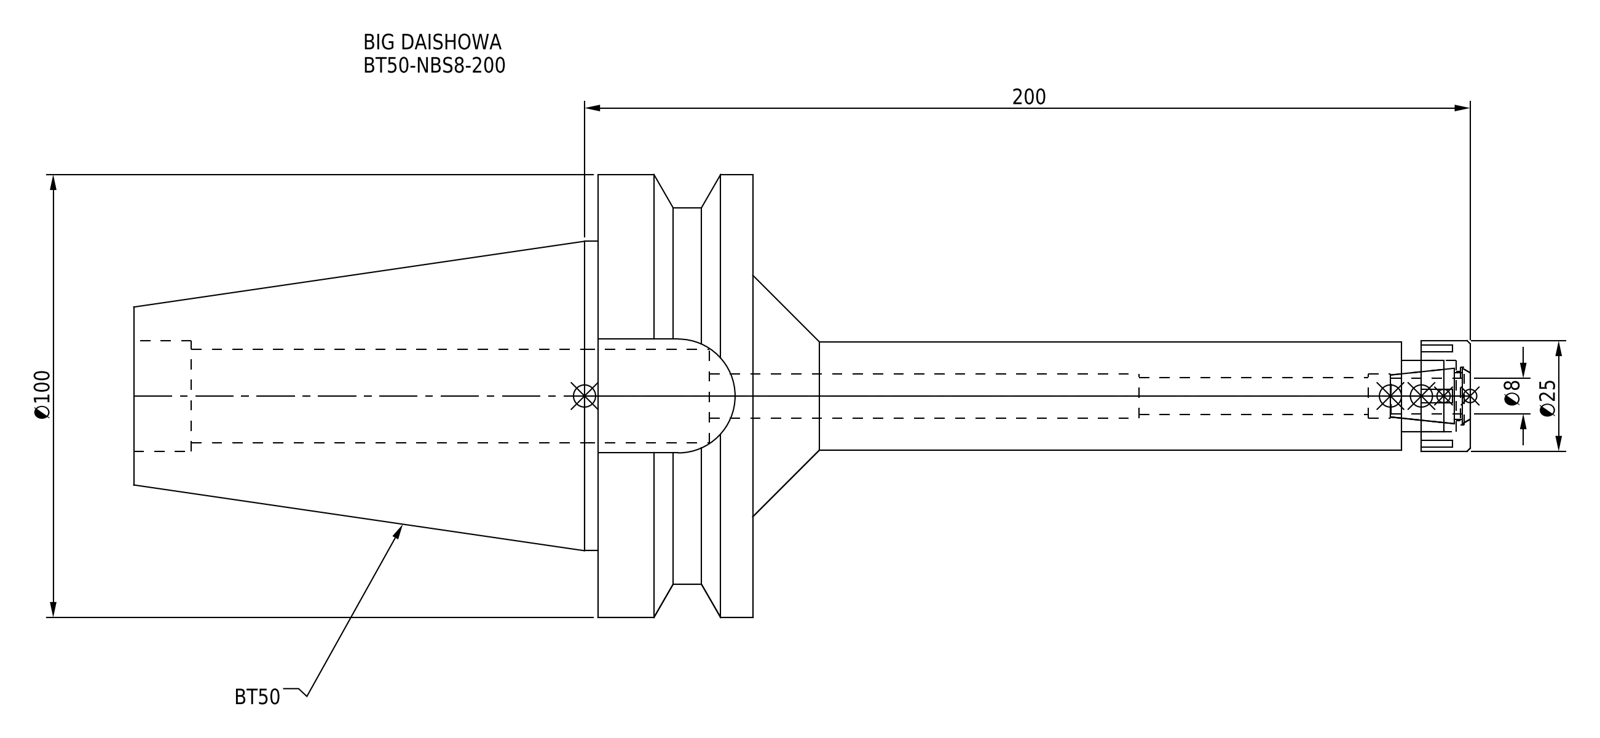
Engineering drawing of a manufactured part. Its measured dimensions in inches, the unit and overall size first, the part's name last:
Units: inches
Overall size (bounding box): 11.882 × 3.937 × 3.937
Round holes (diameter × count): ⌀0.331 ×1, ⌀0.394 ×1, ⌀0.433 ×1, ⌀0.512 ×1, ⌀0.63 ×1, ⌀0.835 ×1, ⌀0.984 ×1
Round bosses / shafts (diameter × count): ⌀3.937 ×1, ⌀3.346 ×1, ⌀2.75 ×1, ⌀0.965 ×1
Partial cylindrical surfaces — rounded edges, fillets, slot ends (radius × count): R0.506 ×1
Main face-to-face distances: 1.378, 5.504, 4.126, 2.787, 1.012, 6.378, 7.756, 11.882, 6.764, 0.386
Volume: 31.78 in³ · Surface area: 112.3 in²
Bodies: 2 solids, 93 faces (45 planar, 34 cylindrical, 14 other)
Part name (STEP PRODUCT): BT50-NBS8-200; BT50-NBS8-200-FreeParts; BT50NB08200-080_ASM.stp; DXF_TEMP_ASSY_ASM_4_ASM.stp (+3 more)
STEP written by: SolidWorks 2019 (CONFIG_CONTROL_DESIGN)
